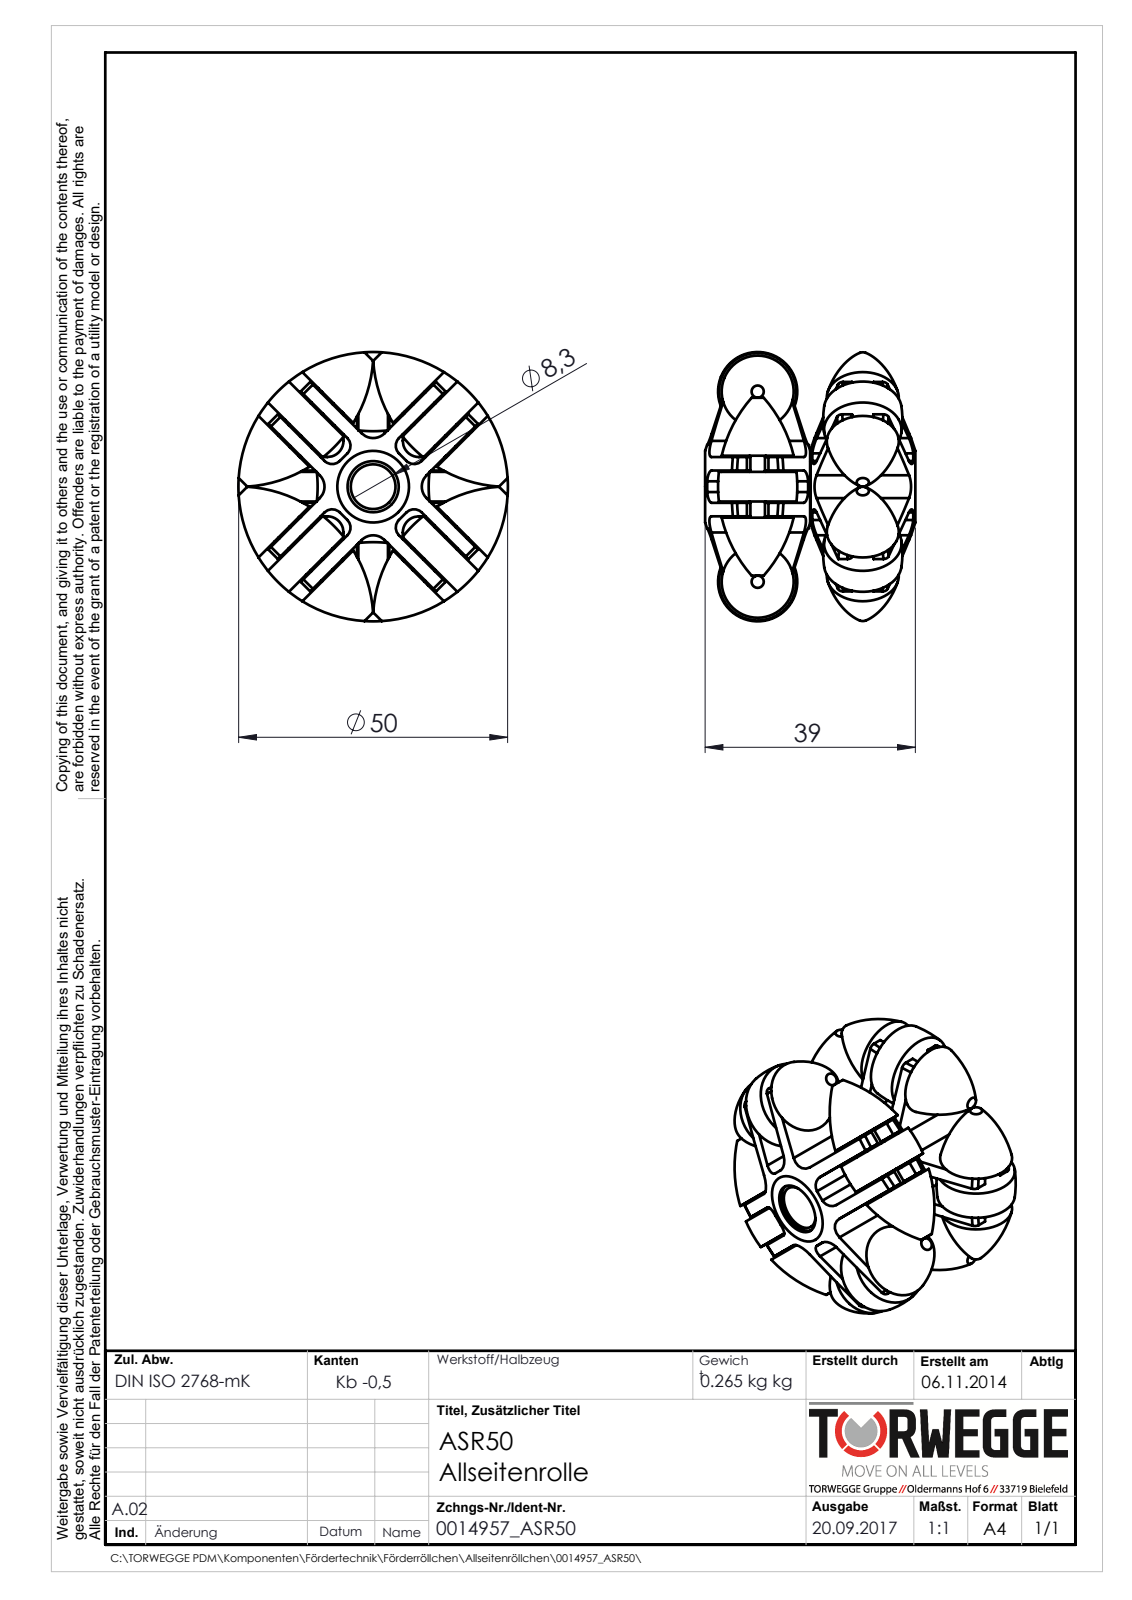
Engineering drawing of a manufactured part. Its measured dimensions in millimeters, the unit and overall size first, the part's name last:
Units: millimetres
Overall size (bounding box): 50 × 50 × 39
Round holes (diameter × count): ⌀3.1 ×8, ⌀3 ×5, ⌀8.3 ×1, ⌀9.5 ×1, ⌀10.3 ×1, ⌀13.3 ×1
Round bosses / shafts (diameter × count): ⌀3 ×3
Partial cylindrical surfaces — rounded edges, fillets, slot ends (radius × count): R2 ×16, R3 ×8, R1.5 ×3, R1 ×2
Main face-to-face distances: 2.75, 8.5, 2.5, 3, 8.25, 5.75, 8.75, 11.25, 8.49, 5.5
Hole centre spacings: 35.3
Volume: 33 570 mm³ · Surface area: 26 980 mm²
Bodies: 34 solids, 462 faces (222 planar, 122 cylindrical, 118 other)
Part name (STEP PRODUCT): 0014873_ASR10; ASR10_Halter; ASR50_Rolle_Steg; ASR10_Achse (+3 more)
STEP written by: SolidWorks 2016 (AUTOMOTIVE_DESIGN)
